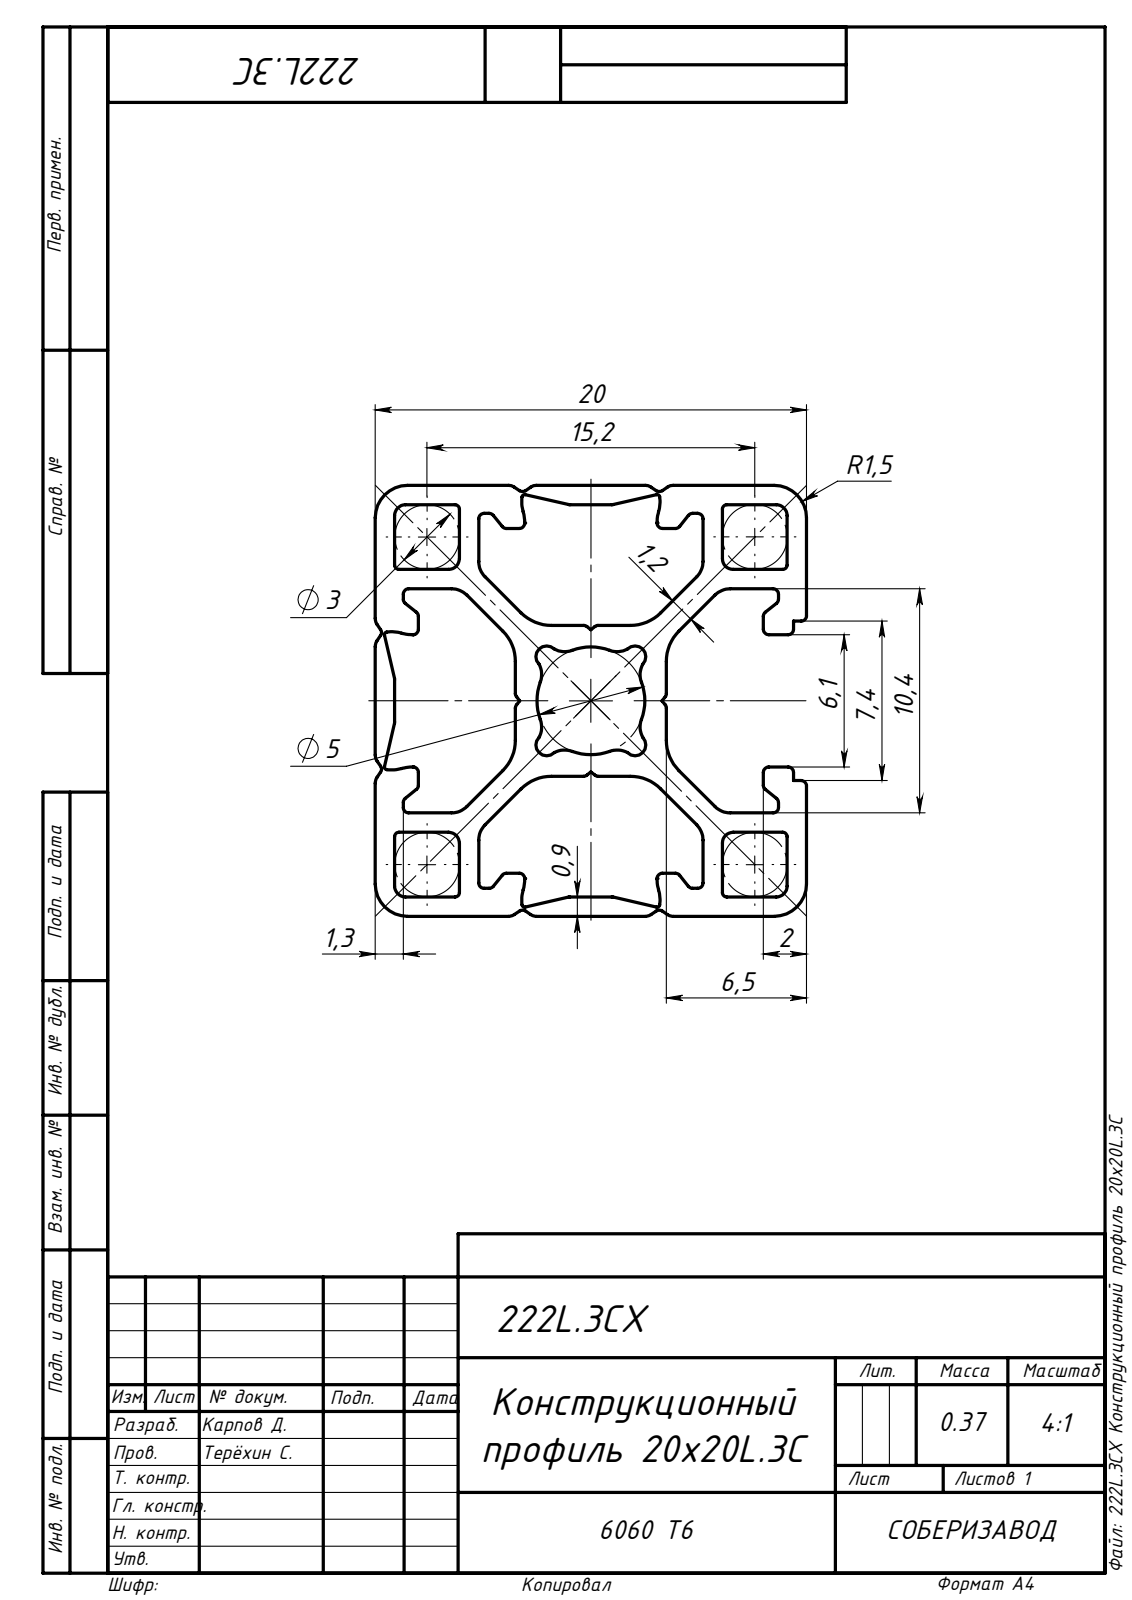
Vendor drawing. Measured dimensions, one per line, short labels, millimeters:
written by: SolidWorks 2019 (AUTOMOTIVE_DESIGN)
unit: mm
bodies: 1 solid, 256 faces (118 planar, 138 cylindrical, 0 other)
size: 1000 × 20 × 20
volume: 135 725 mm³; area: 259 014 mm²
rounds: 56× R0.25, 24× R0.5, 16× R1, 14× R2, 8× R0.2, 6× R0.12, 6× R1.8, 4× R1.5
face distances: 0.9, 3.9, 15.2, 19.1, 20, 16.1, 3, 4.8, 14.3, 11.3
